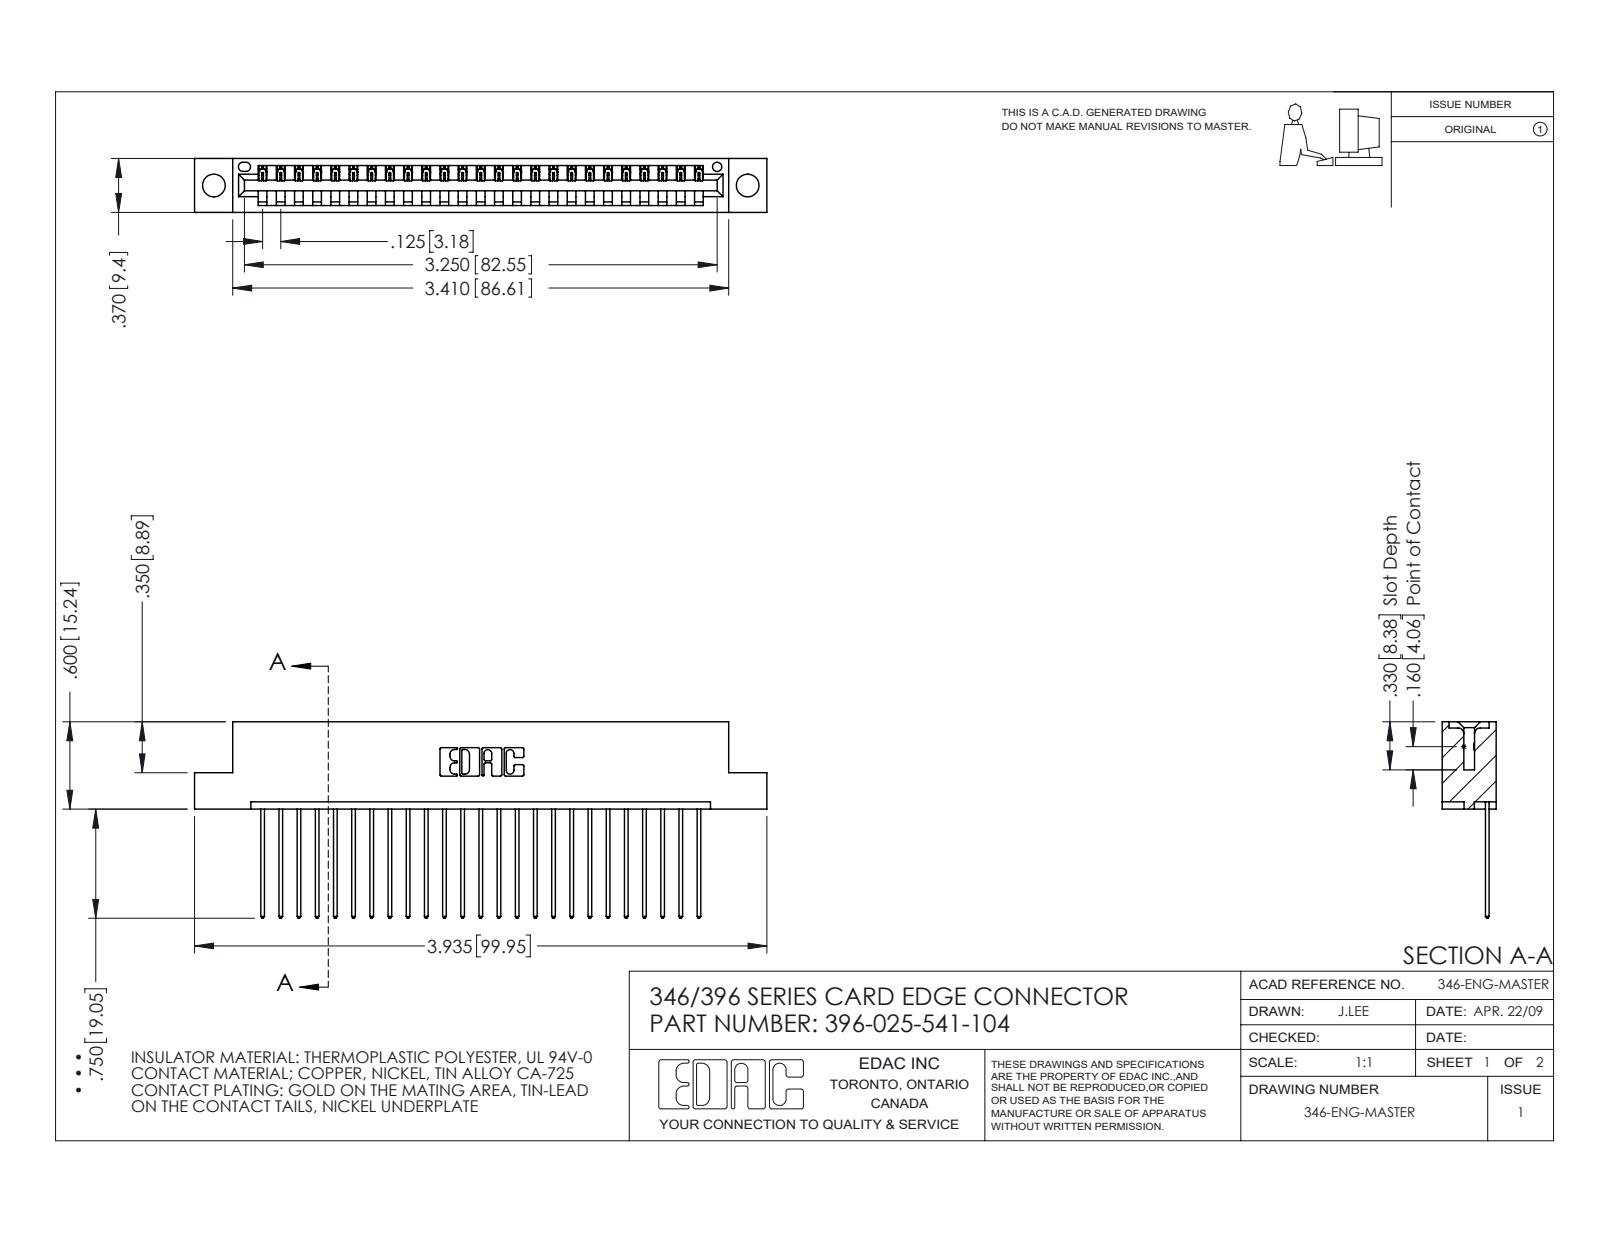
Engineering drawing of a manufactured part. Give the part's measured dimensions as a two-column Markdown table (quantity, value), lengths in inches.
| quantity | value |
| --- | --- |
| part name | 345-292-001_345-293-141; 346 Part_Flush Mounting Lugs - 0.156 Dia-TH; 396-025-541-104 |
| STEP written by | SolidWorks 2016 (CONFIG_CONTROL_DESIGN) |
| units | inches |
| bodies | 26 solids, 1572 faces (1076 planar, 496 cylindrical, 0 other) |
| overall size | 3.935 × 1.35 × 0.37 |
| volume | 0.576 in³ |
| surface area | 18.47 in² |
| round holes (diameter × count) | 0.156 × 2, 0.064 × 1 |
| partial cylindrical surfaces (radius × count) | 0.006 × 50, 0.01 × 50, 0.01 × 22, 0.007 × 6, 0.031 × 6, 0.026 × 3, 0.031 × 2, 0.04 × 2 |
| main face-to-face distances | 0.048, 0.322, 0.37, 0.25, 0.072, 0.298, 0.025, 0.148, 0.222, 0.1 |
| hole center spacings | 0.246, 3.462, 3.67 |
